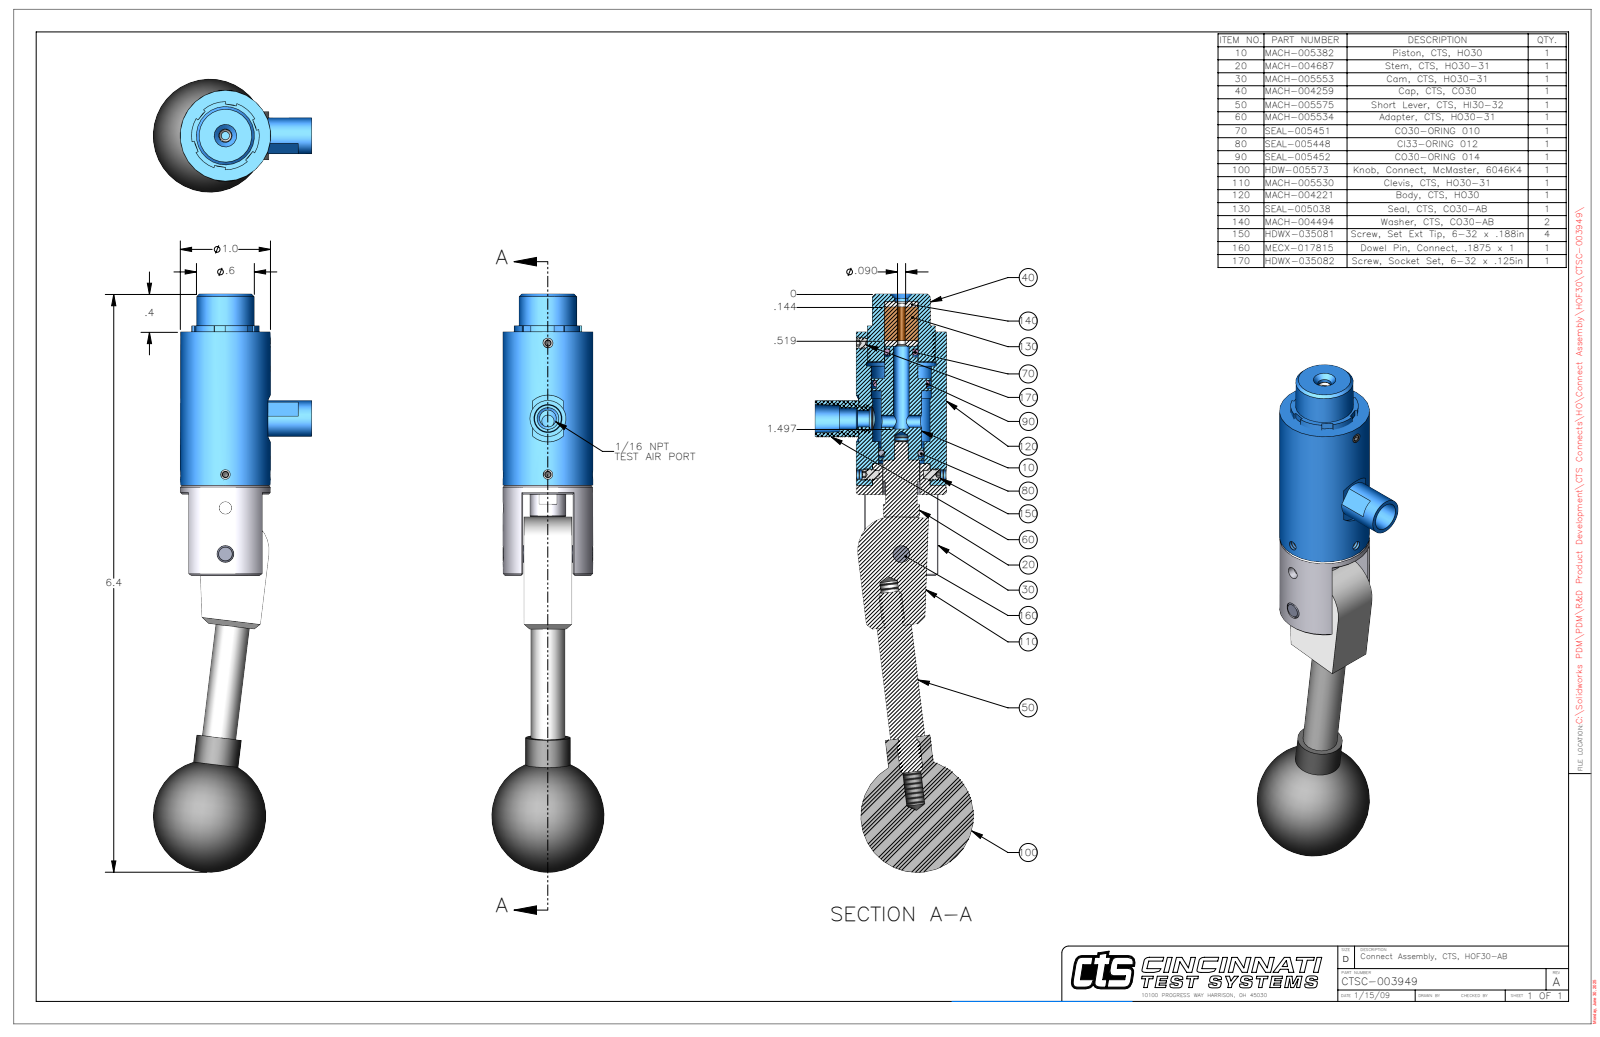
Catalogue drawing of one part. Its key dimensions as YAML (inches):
part_name: "CTSC-003949"
step_written_by: "SolidWorks 2023 (AUTOMOTIVE_DESIGN)"
units: inches
bodies: {solids: 13, faces: 460, planar: 168, cylindrical: 161, other: 131}
overall_size: [6.407, 1.755, 1.25]
volume: 3.401
surface_area: 32.73
round_holes:
  - {diameter: 0.107, count: 3}
  - {diameter: 0.201, count: 2}
  - {diameter: 0.09, count: 1}
  - {diameter: 0.092, count: 1}
  - {diameter: 0.136, count: 1}
  - {diameter: 0.138, count: 1}
  - {diameter: 0.15, count: 1}
  - {diameter: 0.15, count: 1}
  - {diameter: 0.175, count: 1}
  - {diameter: 0.187, count: 1}
  - {diameter: 0.189, count: 1}
  - {diameter: 0.19, count: 1}
round_bosses_or_shafts:
  - {diameter: 0.138, count: 3}
  - {diameter: 0.4, count: 2}
  - {diameter: 0.092, count: 2}
  - {diameter: 1, count: 1}
  - {diameter: 0.642, count: 1}
  - {diameter: 0.63, count: 1}
  - {diameter: 0.5, count: 1}
  - {diameter: 0.49, count: 1}
partial_cylinders:
  - {radius: 0.26, count: 1}
  - {radius: 0.349, count: 1}
  - {radius: 0.374, count: 1}
  - {radius: 0.375, count: 1}
face_to_face_distances: [0.012, 0.542, 0.53, 0.554, 1.8, 0.059, 0.434, 1.241, 2.22, 0.42]
hole_center_spacings: [0.03, 0.37, 0.51, 0.59, 0.62, 0.835, 0.865, 0.88]
